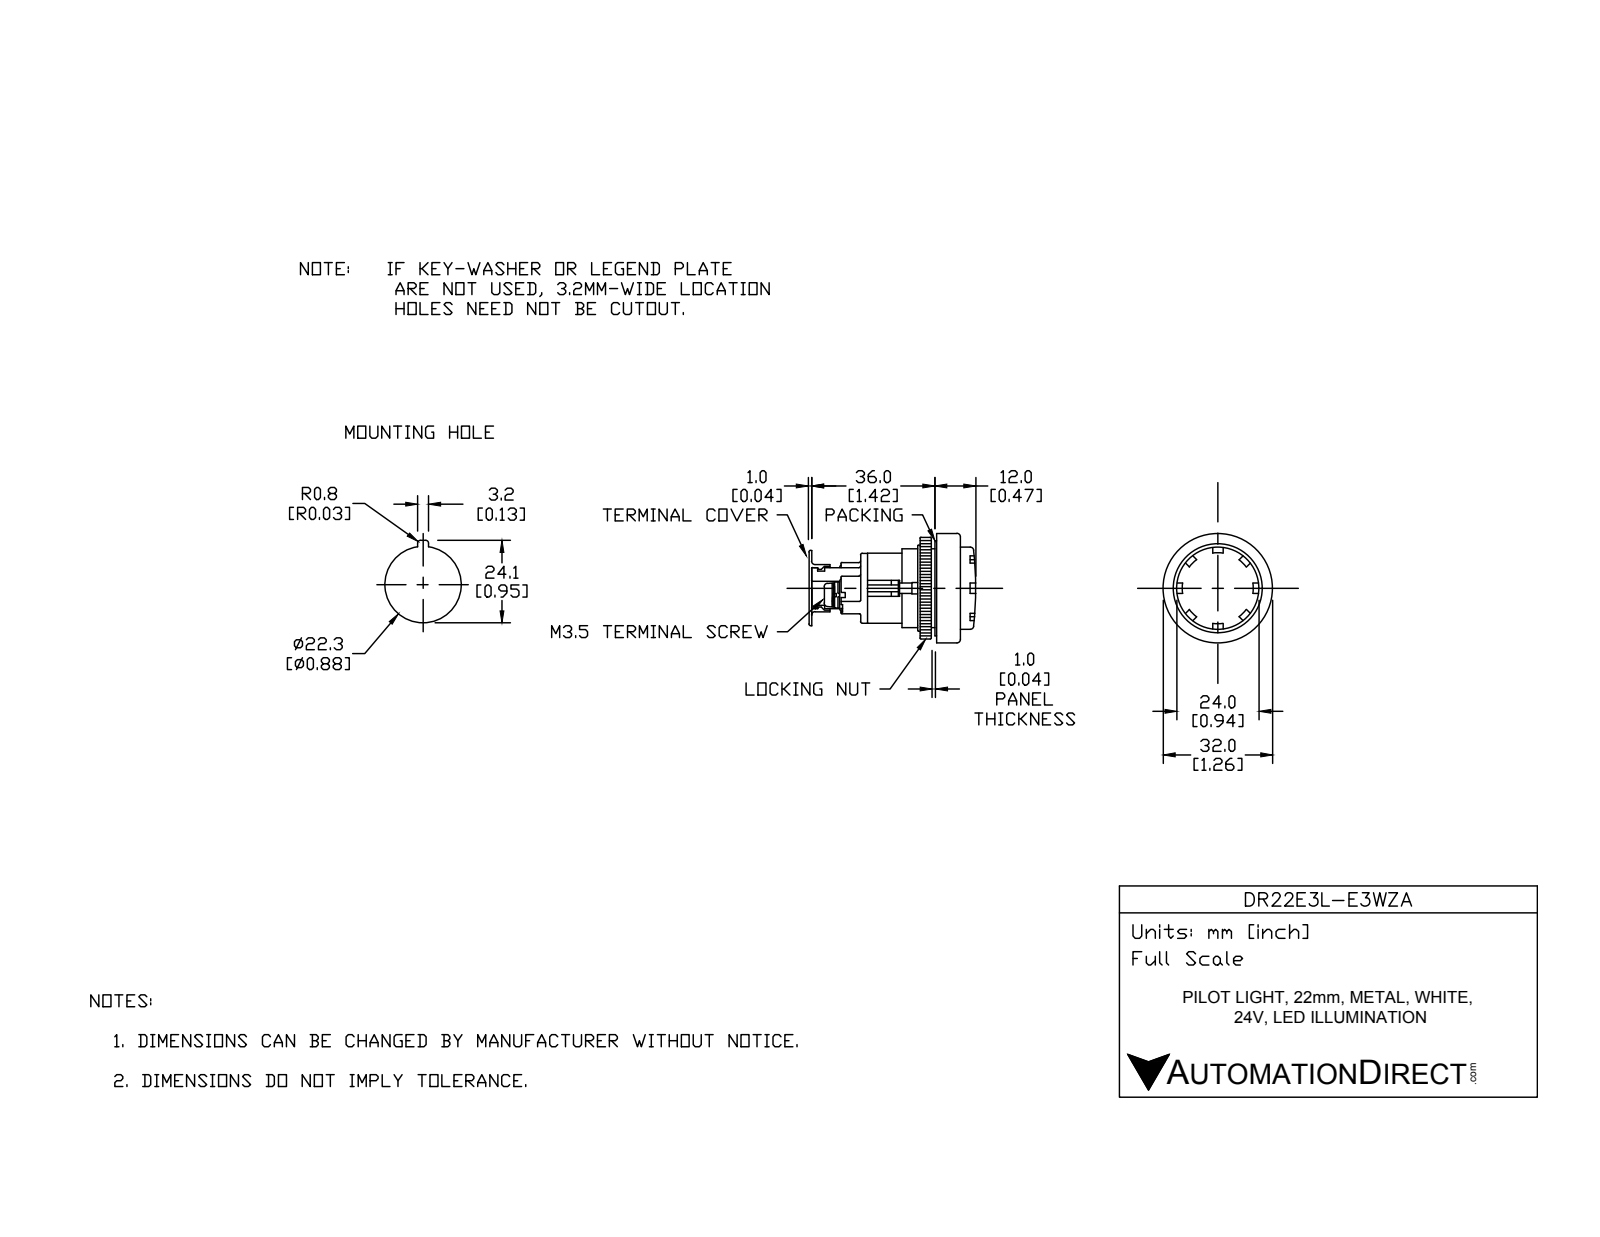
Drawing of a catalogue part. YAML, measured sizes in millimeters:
part_name: "DR22E3L-E3WZA"
step_written_by: "SolidWorks 2017 (AUTOMOTIVE_DESIGN)"
units: millimeters
bodies: {solids: 11, faces: 126, planar: 76, cylindrical: 38, other: 12}
overall_size: [48, 32, 32]
volume: 19463
surface_area: 11440
round_holes:
  - {diameter: 6.4, count: 2}
  - {diameter: 22, count: 1}
  - {diameter: 25, count: 1}
  - {diameter: 30, count: 1}
round_bosses_or_shafts:
  - {diameter: 5.8, count: 2}
  - {diameter: 32, count: 1}
  - {diameter: 29.7, count: 1}
  - {diameter: 29.5, count: 1}
  - {diameter: 27, count: 1}
  - {diameter: 21.8, count: 1}
partial_cylinders:
  - {radius: 0.5, count: 8}
face_to_face_distances: [4, 26, 6, 16, 1, 20, 27, 42, 15, 11]
hole_center_spacings: [6.04, 12.08]
